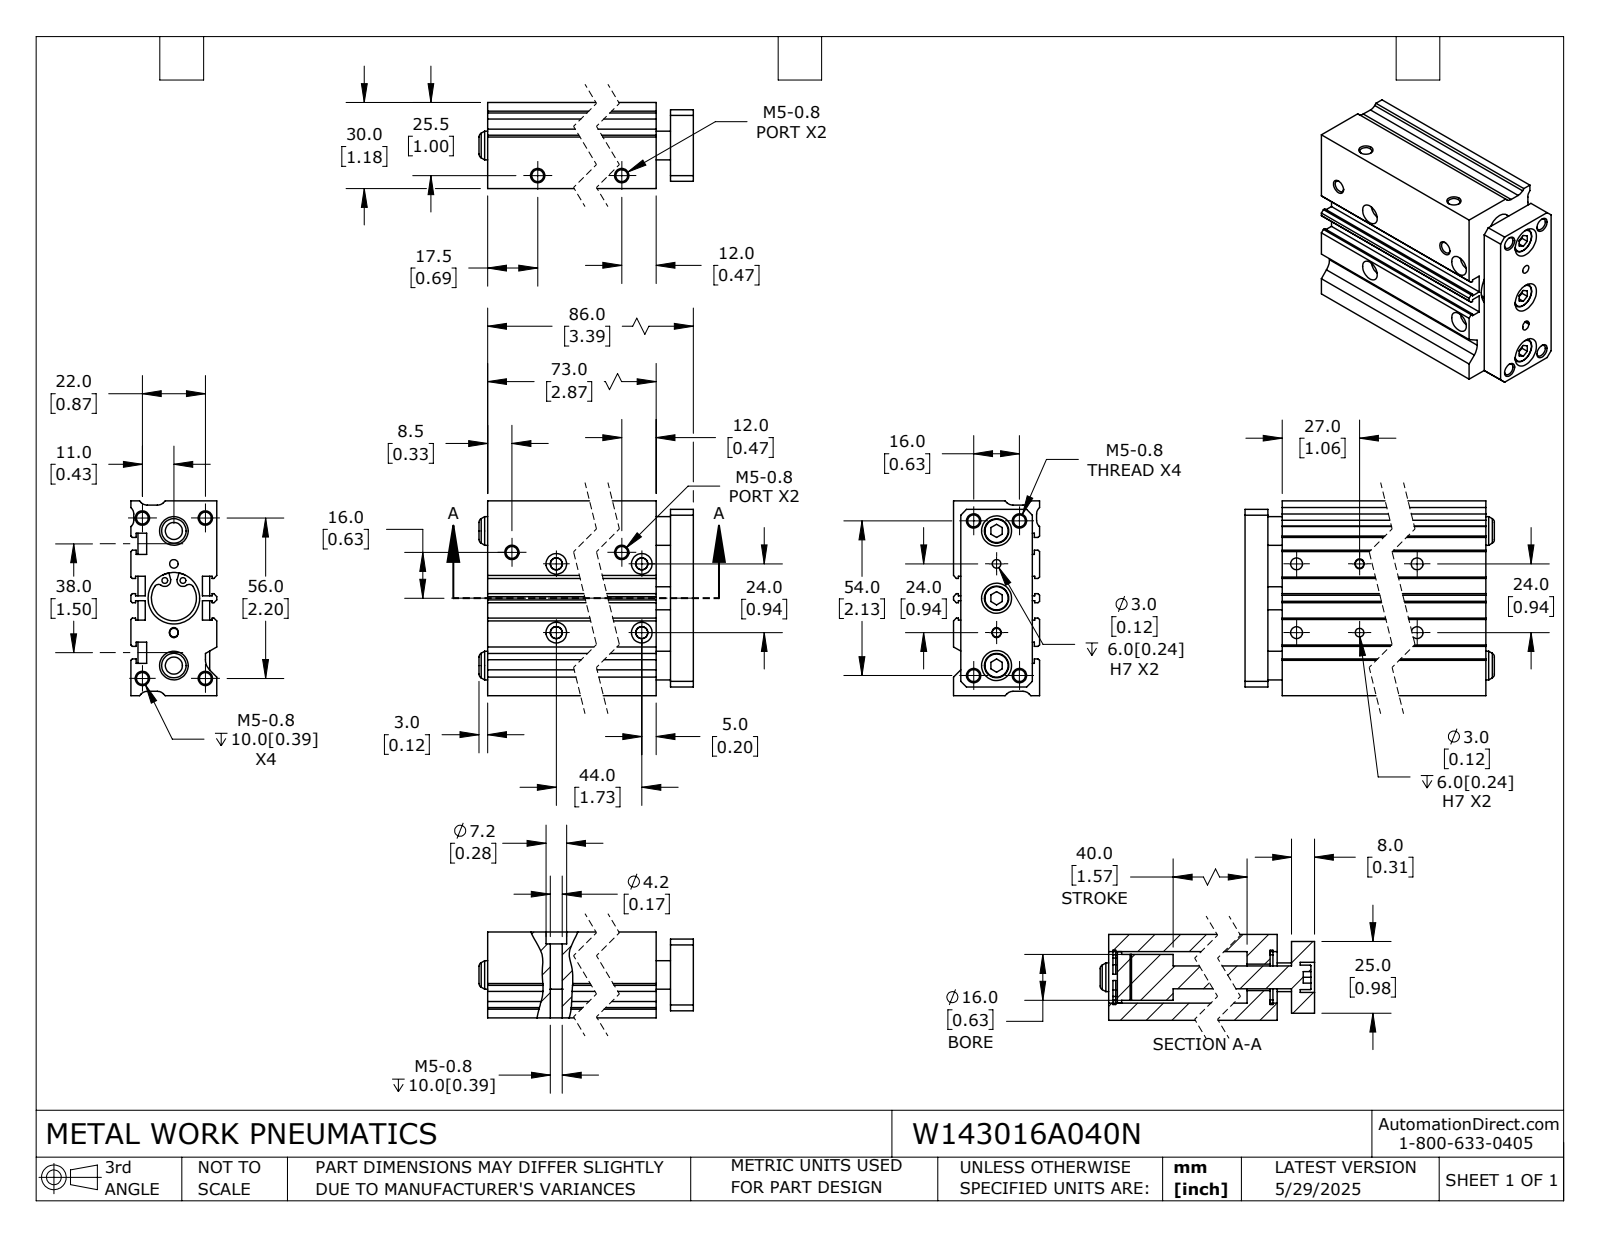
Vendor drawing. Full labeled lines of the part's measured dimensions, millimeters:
Part name (STEP PRODUCT): W143016A040_BODY; W143016A040_ROD; W143016A040N
STEP written by: SolidWorks 2024 (CONFIG_CONTROL_DESIGN)
Units: millimetres
Bodies: 5 solids, 344 faces (169 planar, 137 cylindrical, 38 other)
Overall size (bounding box): 89 × 68 × 30
Volume: 129 318 mm³ · Surface area: 49 620 mm²
Round holes (diameter × count): ⌀4.13 ×16, ⌀2 ×4, ⌀3 ×4, ⌀4.2 ×4, ⌀7.2 ×4, ⌀10.5 ×3, ⌀10 ×2, ⌀9.2 ×1, ⌀15.7 ×1, ⌀18 ×1
Round bosses / shafts (diameter × count): ⌀8.5 ×3, ⌀19 ×2, ⌀16 ×1, ⌀8 ×1
Partial cylindrical surfaces — rounded edges, fillets, slot ends (radius × count): R3 ×6, R1.5 ×4, R1.58 ×4, R2.07 ×4, R5 ×1
Main face-to-face distances: 5, 30, 25, 2.5, 1.5, 8, 68, 78, 73, 3
Hole centre spacings: 22, 3.16, 6.62, 6.95, 8.73, 11.88, 17, 17.6
